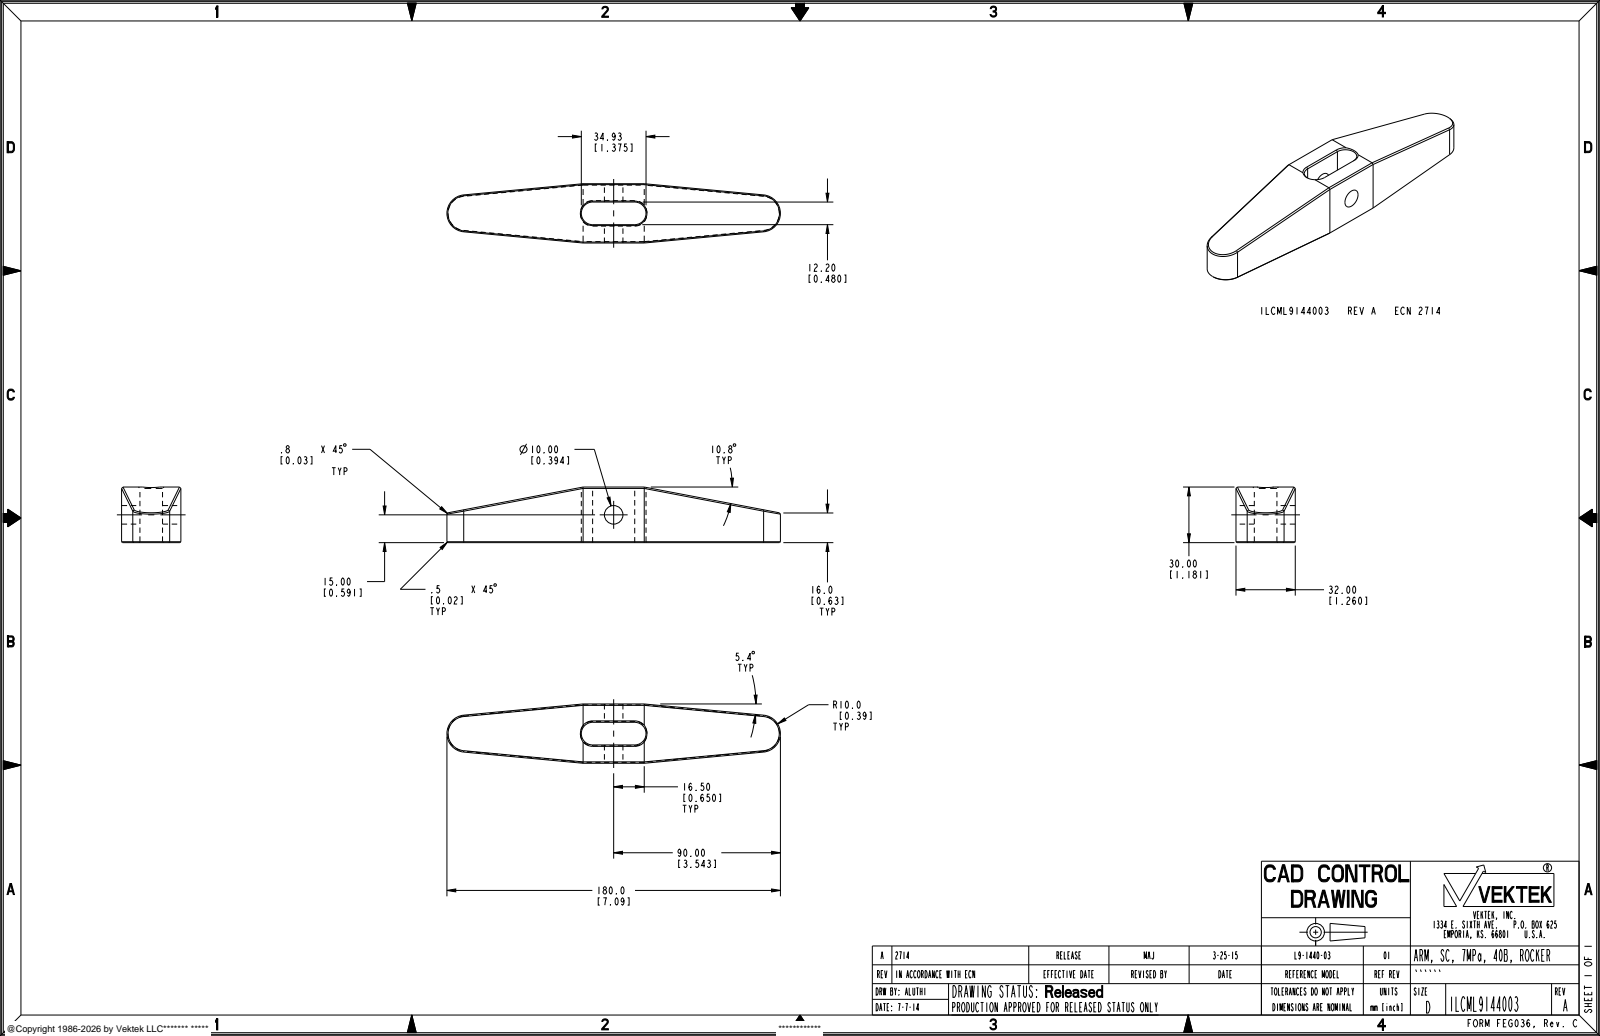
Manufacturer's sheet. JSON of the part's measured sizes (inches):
{"part_name": "ILCML9144003", "step_written_by": "PRO/ENGINEER BY PARAMETRIC TECHNOLOGY CORPORATION, 2013320 (AUTOMOTIVE_DESIGN)", "units": "inches", "bodies": {"solids": 1, "faces": 45, "planar": 29, "cylindrical": 8, "other": 8}, "overall_size": [7.087, 1.26, 1.181], "volume_in3": 6.361, "surface_area_in2": 31.39, "round_holes": [[0.394, 1]], "partial_cylinders_radius": [[0.24, 2], [0.394, 2]], "face_to_face_distances": [1.376, 1.373, 0.39, 0.87, 1.26, 0.48, 1.181, 0.615, 1.691, 1.076]}
